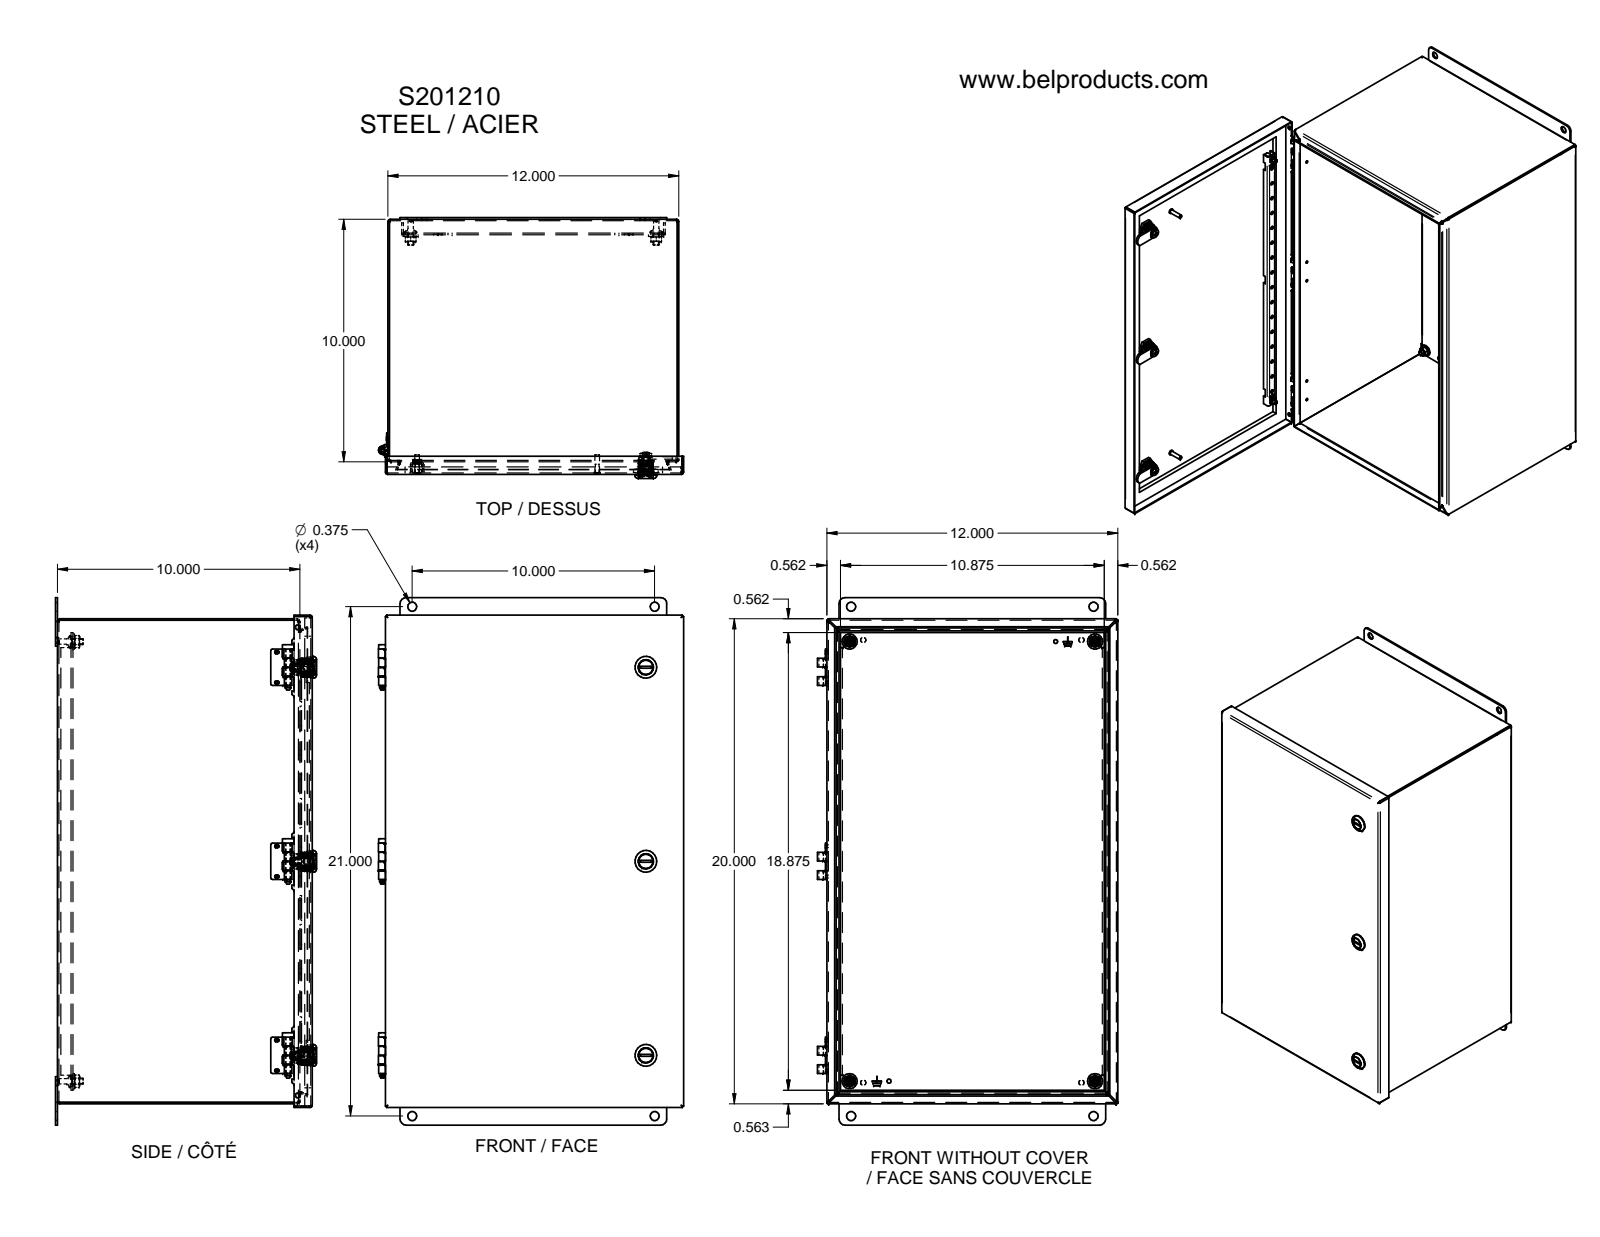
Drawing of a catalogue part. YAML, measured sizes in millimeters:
part_name: "LOCK AVEC TOURNEVIS TYPE 4-12 SANS CAME-oa8; HOSING-oa0; INSERT POUR TOURNEVIS-oa1; NOIX DE FIXATION-oa2 (+8 more)"
step_written_by: "Unknown (AUTOMOTIVE_DESIGN)"
units: millimeters
bodies: {solids: 60, faces: 3255, planar: 1859, cylindrical: 627, other: 769}
overall_size: [552.45, 319.75, 273.44]
volume: 1755000
surface_area: 2060000
round_holes:
  - {diameter: 4.09, count: 16}
  - {diameter: 3.17, count: 8}
  - {diameter: 3.16, count: 6}
  - {diameter: 3.3, count: 6}
  - {diameter: 5.59, count: 5}
  - {diameter: 0.35, count: 4}
  - {diameter: 5.99, count: 4}
  - {diameter: 6.35, count: 4}
  - {diameter: 7.14, count: 4}
  - {diameter: 9.53, count: 4}
  - {diameter: 11.1, count: 4}
  - {diameter: 6.99, count: 3}
round_bosses_or_shafts:
  - {diameter: 3.02, count: 8}
  - {diameter: 3.17, count: 6}
  - {diameter: 15.88, count: 4}
  - {diameter: 6.5, count: 4}
  - {diameter: 5.71, count: 4}
  - {diameter: 5.56, count: 4}
  - {diameter: 4.83, count: 4}
  - {diameter: 0.79, count: 4}
partial_cylinders:
  - {radius: 0.4, count: 34}
  - {radius: 1.59, count: 32}
  - {radius: 9.53, count: 32}
  - {radius: 0.25, count: 24}
  - {radius: 0.81, count: 21}
  - {radius: 2.34, count: 19}
  - {radius: 0.79, count: 13}
  - {radius: 0.79, count: 12}
face_to_face_distances: [1.52, 303.28, 265.54, 1.53, 267.07, 264.02, 265.55, 506.48, 16.27, 1.91]
hole_center_spacings: [14.38, 203.2, 228.6, 406.39, 242.9, 1.57, 25.4, 33.95]
